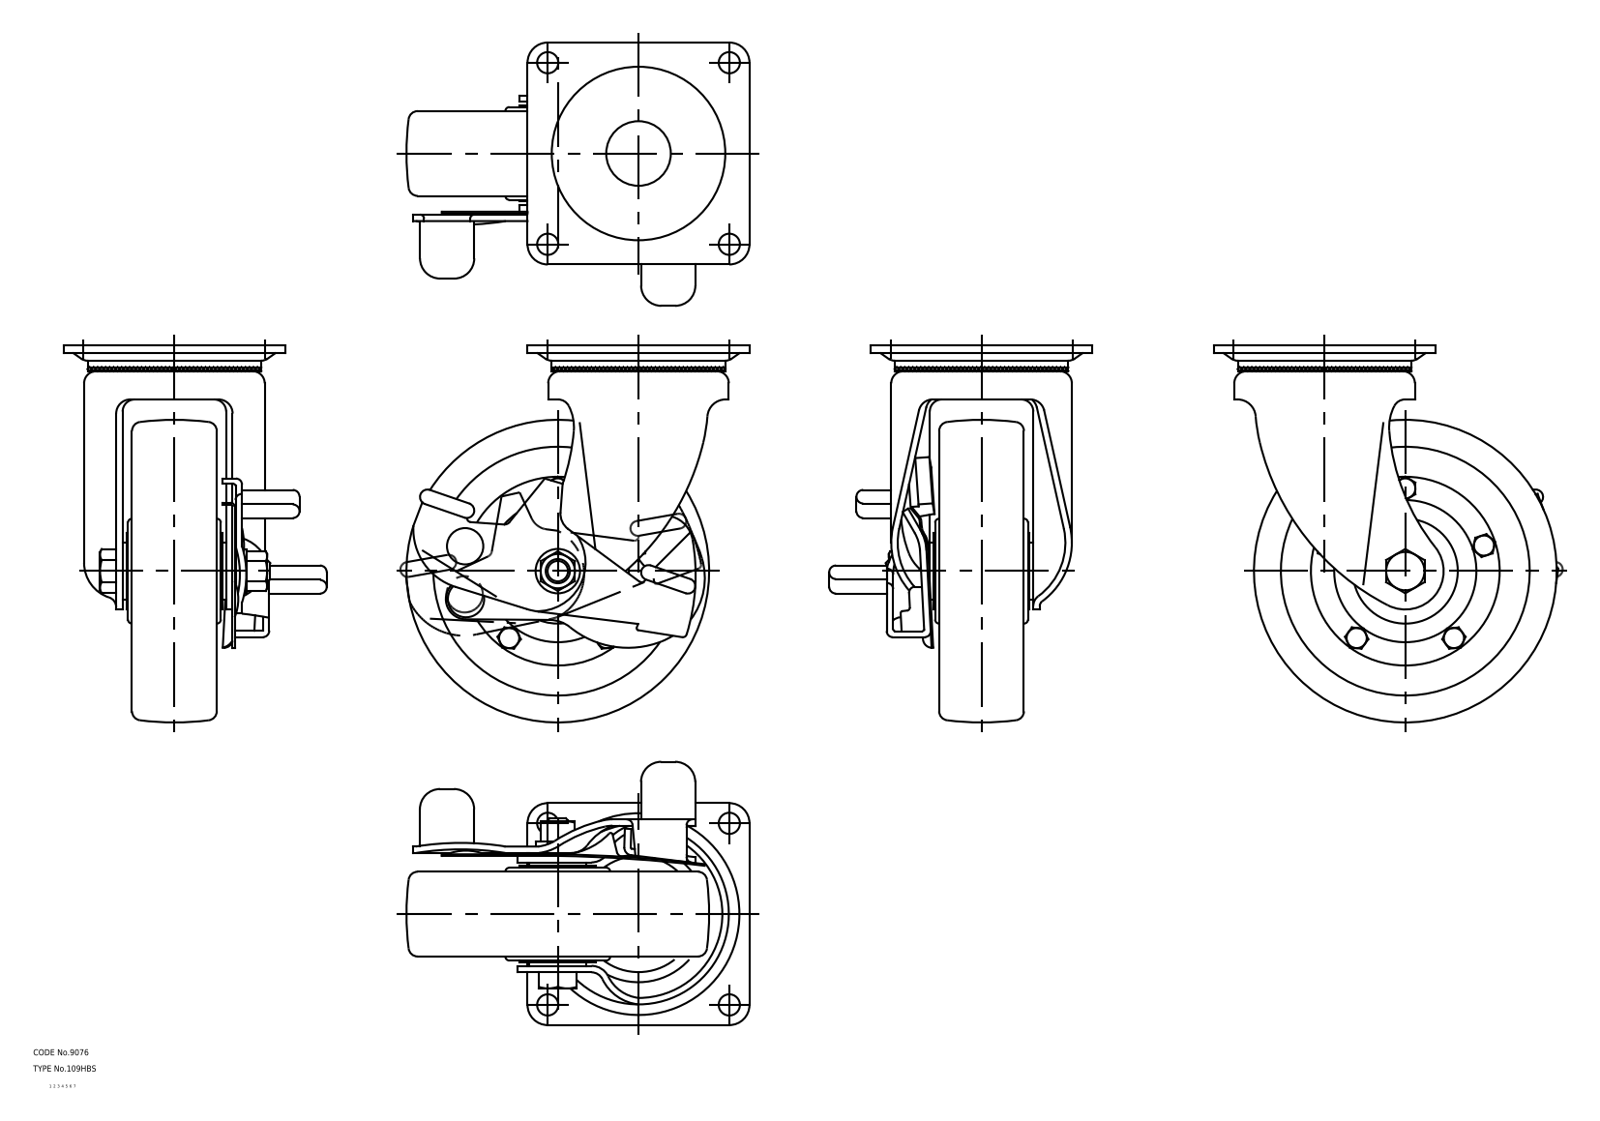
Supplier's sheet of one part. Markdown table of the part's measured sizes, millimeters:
| quantity | value |
| --- | --- |
| part name | 67141983; 67141996; 67142009; 67142022 (+5 more) |
| STEP written by | CADfix (AUTOMOTIVE_DESIGN) |
| units | millimeters |
| bodies | 6 solids, 570 faces (0 planar, 0 cylindrical, 570 other) |
| overall size | 187 × 170 × 130.5 |
| volume | 869 325 mm³ |
| surface area | 178 501 mm² |
